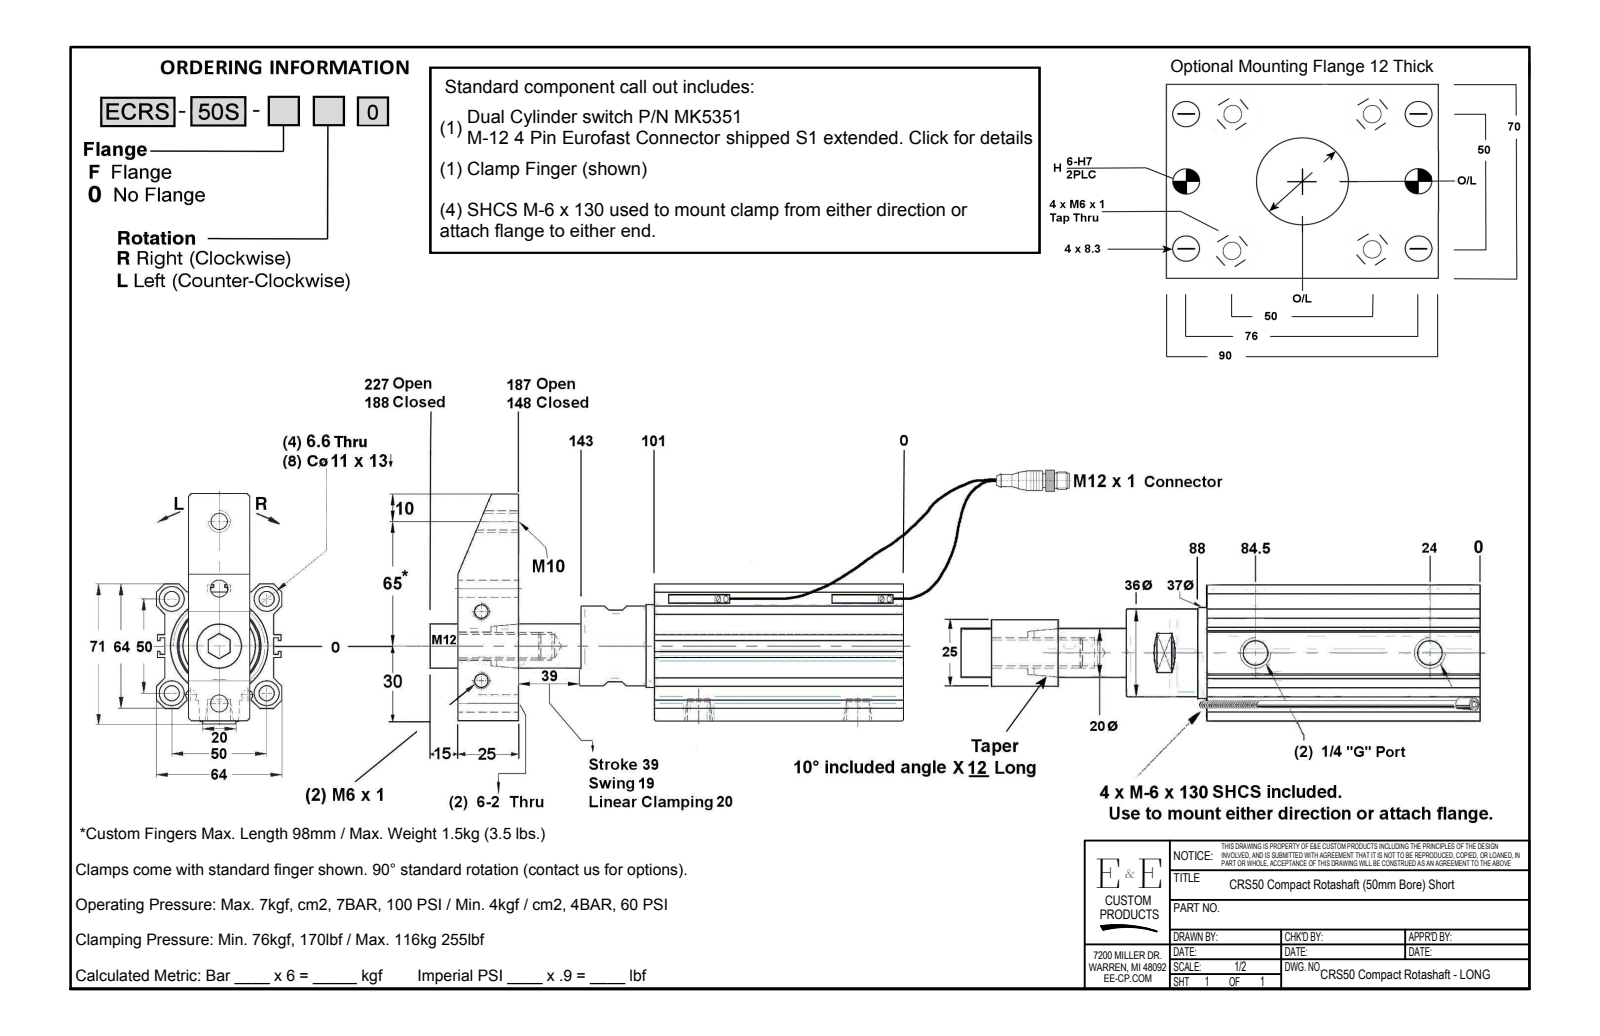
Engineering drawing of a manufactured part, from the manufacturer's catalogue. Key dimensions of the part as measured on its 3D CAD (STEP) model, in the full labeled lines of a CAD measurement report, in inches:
Part name (STEP PRODUCT): PBS-50_Shrinkwrap_1
STEP written by: Autodesk Inventor 2018 (AUTOMOTIVE_DESIGN)
Units: inches
Bodies: 7 solids, 248 faces (130 planar, 78 cylindrical, 40 other)
Overall size (bounding box): 7.106 × 4.48 × 2.52
Volume: 21.59 in³ · Surface area: 164.6 in²
Round holes (diameter × count): ⌀0.26 ×4, ⌀0.433 ×4, ⌀0.079 ×2, ⌀0.197 ×2, ⌀0.217 ×2, ⌀0.244 ×2, ⌀0.315 ×2, ⌀0.354 ×1, ⌀0.413 ×1, ⌀0.492 ×1, ⌀0.787 ×1, ⌀1.969 ×1
Round bosses / shafts (diameter × count): ⌀1.969 ×1, ⌀1.457 ×1, ⌀1.417 ×1, ⌀0.748 ×1, ⌀0.63 ×1, ⌀0.472 ×1, ⌀0.417 ×1
Partial cylindrical surfaces — rounded edges, fillets, slot ends (radius × count): R0.008 ×14, R0.079 ×2, R1.693 ×1
Main face-to-face distances: 0.118, 2.402, 2.283, 0.984, 2.52, 2.795, 0.906, 2.362, 0.647, 1.637
Hole centre spacings: 1.392, 1.969, 0.913, 2.784, 0.905, 0.922, 0.983, 0.985
